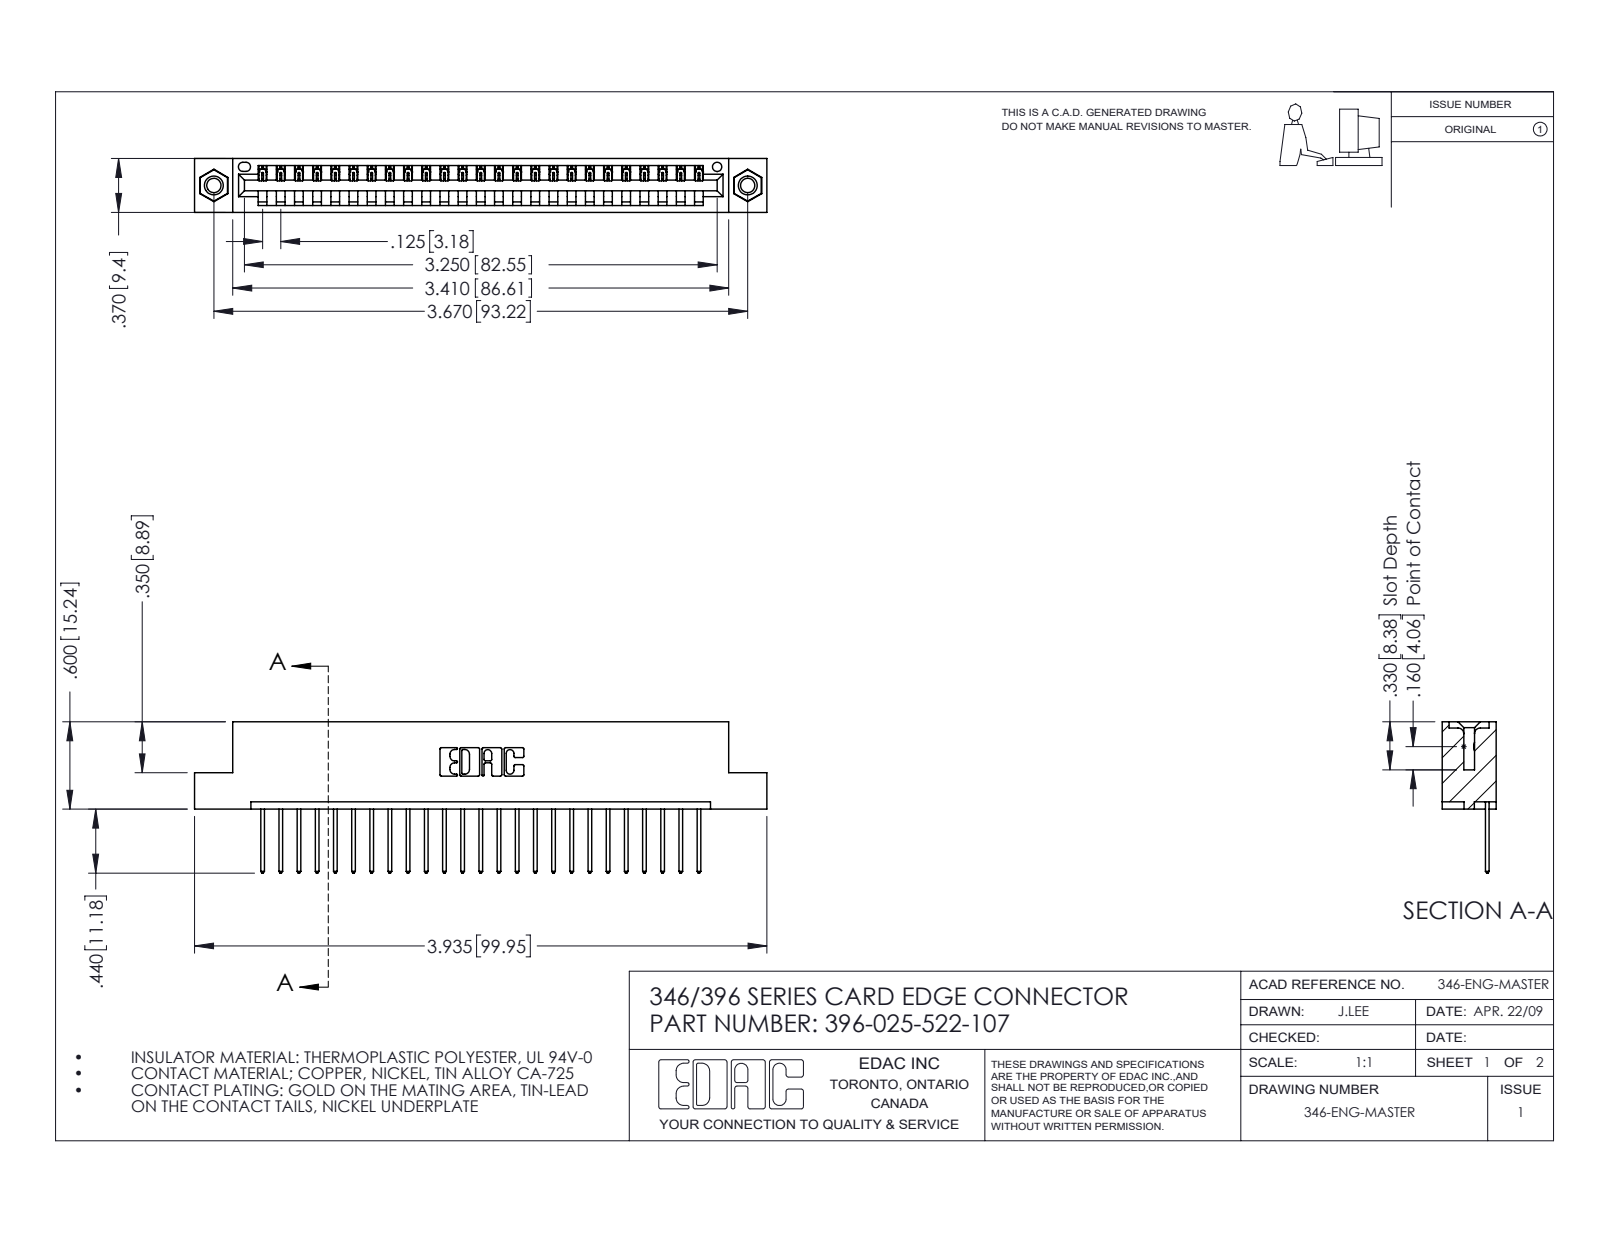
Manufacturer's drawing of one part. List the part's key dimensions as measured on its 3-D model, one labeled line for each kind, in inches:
Part name (STEP PRODUCT): 346 Part_Flush Mounting Lugs - 0.156 Dia-TI; 396-025-522-107; 345-292-001_345-293-122; 345-250-001_345-250-005-103
STEP written by: SolidWorks 2016 (CONFIG_CONTROL_DESIGN)
Units: inches
Bodies: 28 solids, 1632 faces (1108 planar, 508 cylindrical, 16 other)
Overall size (bounding box): 3.935 × 1.04 × 0.37
Volume: 0.576 in³ · Surface area: 18.2 in²
Round holes (diameter × count): ⌀0.098 ×2, ⌀0.125 ×2, ⌀0.156 ×2, ⌀0.064 ×1
Round bosses / shafts (diameter × count): ⌀0.155 ×2
Partial cylindrical surfaces — rounded edges, fillets, slot ends (radius × count): R0.006 ×50, R0.01 ×50, R0.01 ×22, R0.007 ×6, R0.031 ×6, R0.026 ×3, R0.031 ×2, R0.04 ×2
Main face-to-face distances: 0.048, 0.322, 0.37, 0.25, 0.072, 0.298, 0.025, 0.148, 0.222, 0.1
Hole centre spacings: 0.246, 3.462, 3.67
